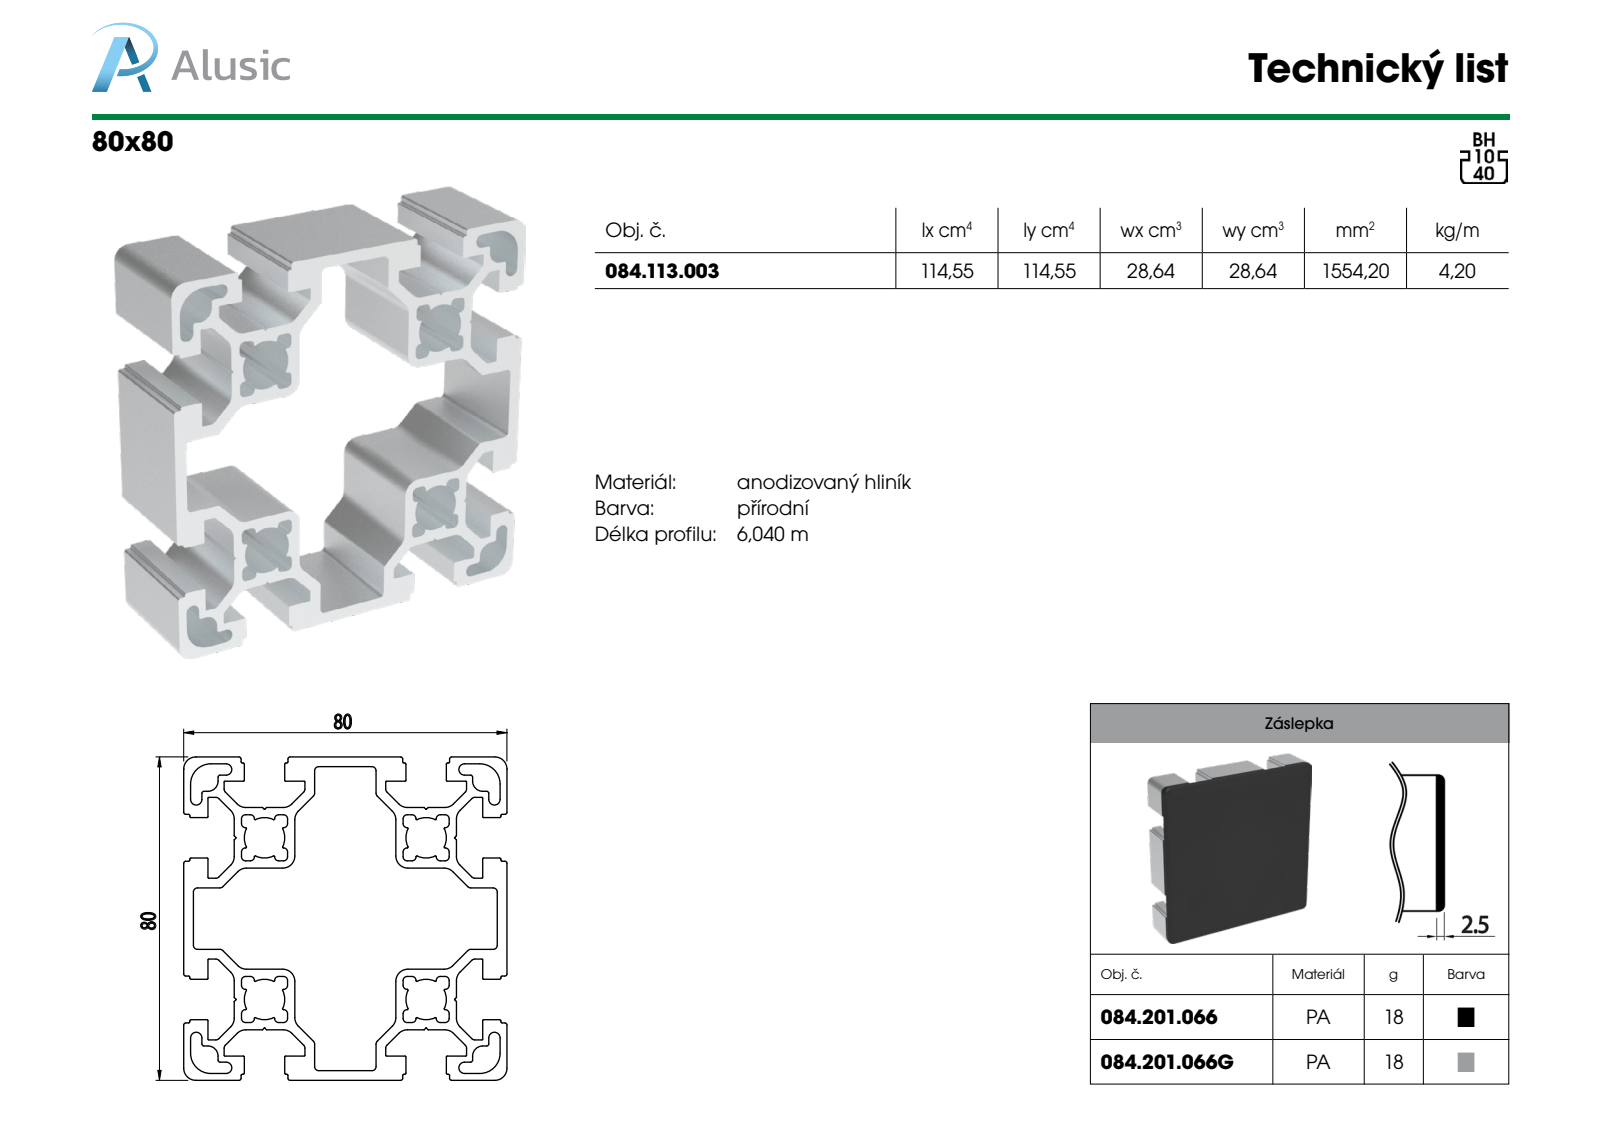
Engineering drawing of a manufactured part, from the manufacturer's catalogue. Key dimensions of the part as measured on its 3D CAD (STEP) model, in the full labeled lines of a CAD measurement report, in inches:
Part name (STEP PRODUCT): 084.113.003
STEP written by: SolidWorks 2018 (AUTOMOTIVE_DESIGN)
Units: inches
Bodies: 1 solid, 562 faces (258 planar, 304 cylindrical, 0 other)
Overall size (bounding box): 3.937 × 3.15 × 3.15
Volume: 9.484 in³ · Surface area: 196.1 in²
Partial cylindrical surfaces — rounded edges, fillets, slot ends (radius × count): R0.039 ×80, R0.008 ×64, R0.012 ×32, R0.118 ×32, R0.004 ×24, R0.02 ×24, R0.055 ×8, R0.197 ×8
Main face-to-face distances: 0.492, 1.083, 2.067, 1.575, 3.15, 0.591, 0.094, 0.236, 2.913, 0.846
